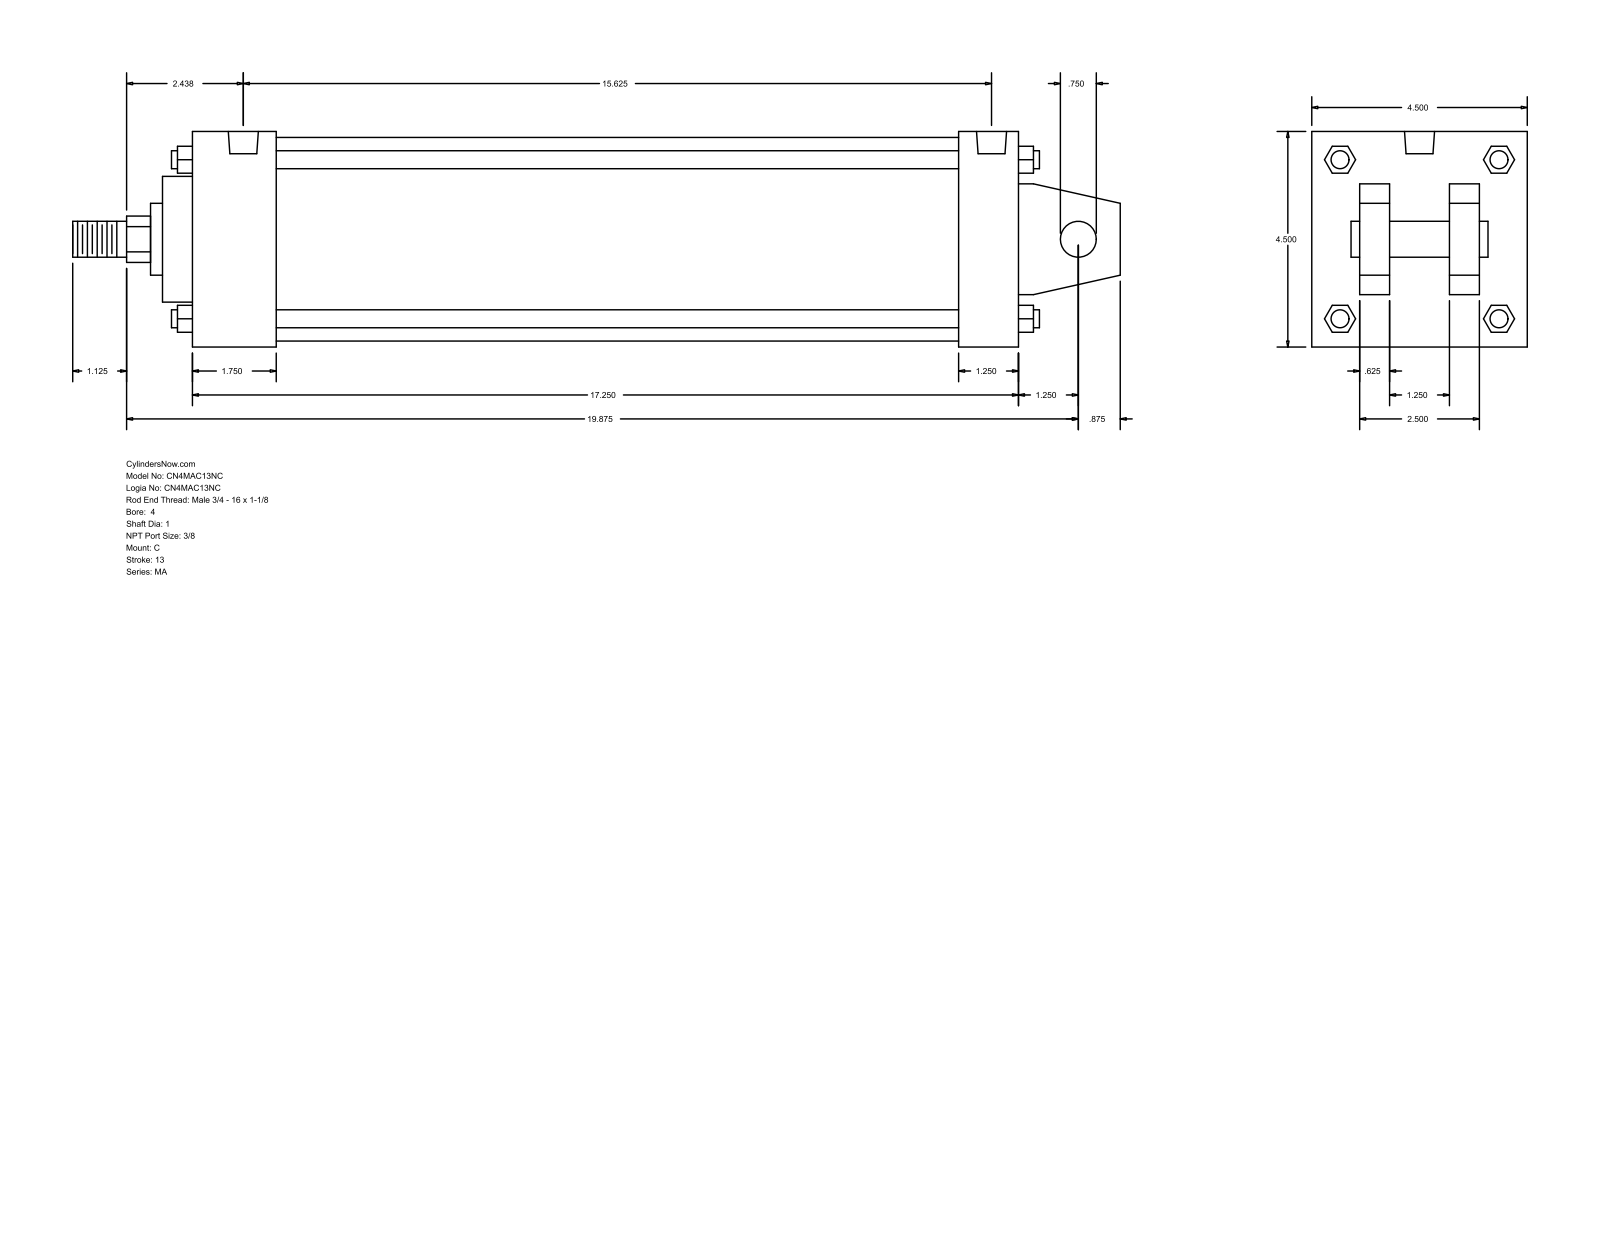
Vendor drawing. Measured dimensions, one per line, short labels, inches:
name: MA_C__0400_1
written by: GSSL Pune (CONFIG_CONTROL_DESIGN)
unit: in
bodies: 0 solids, 141 faces (109 planar, 32 cylindrical, 0 other)
size: 21.875 × 4.5 × 4.5
holes: 4× ⌀0.437, 2× ⌀0.627
bosses: 4× ⌀0.375, 2× ⌀0.75, 1× ⌀4.25, 1× ⌀2.625, 1× ⌀1.5, 1× ⌀1
rounds: 1× R0.484
face distances: 4.5, 17.25, 0.625, 2.875, 1.625, 1, 3.5, 1.875, 16, 1.25
hole spacings: 15.25, 0.187, 0.188, 15.437, 15.438, 15.625
